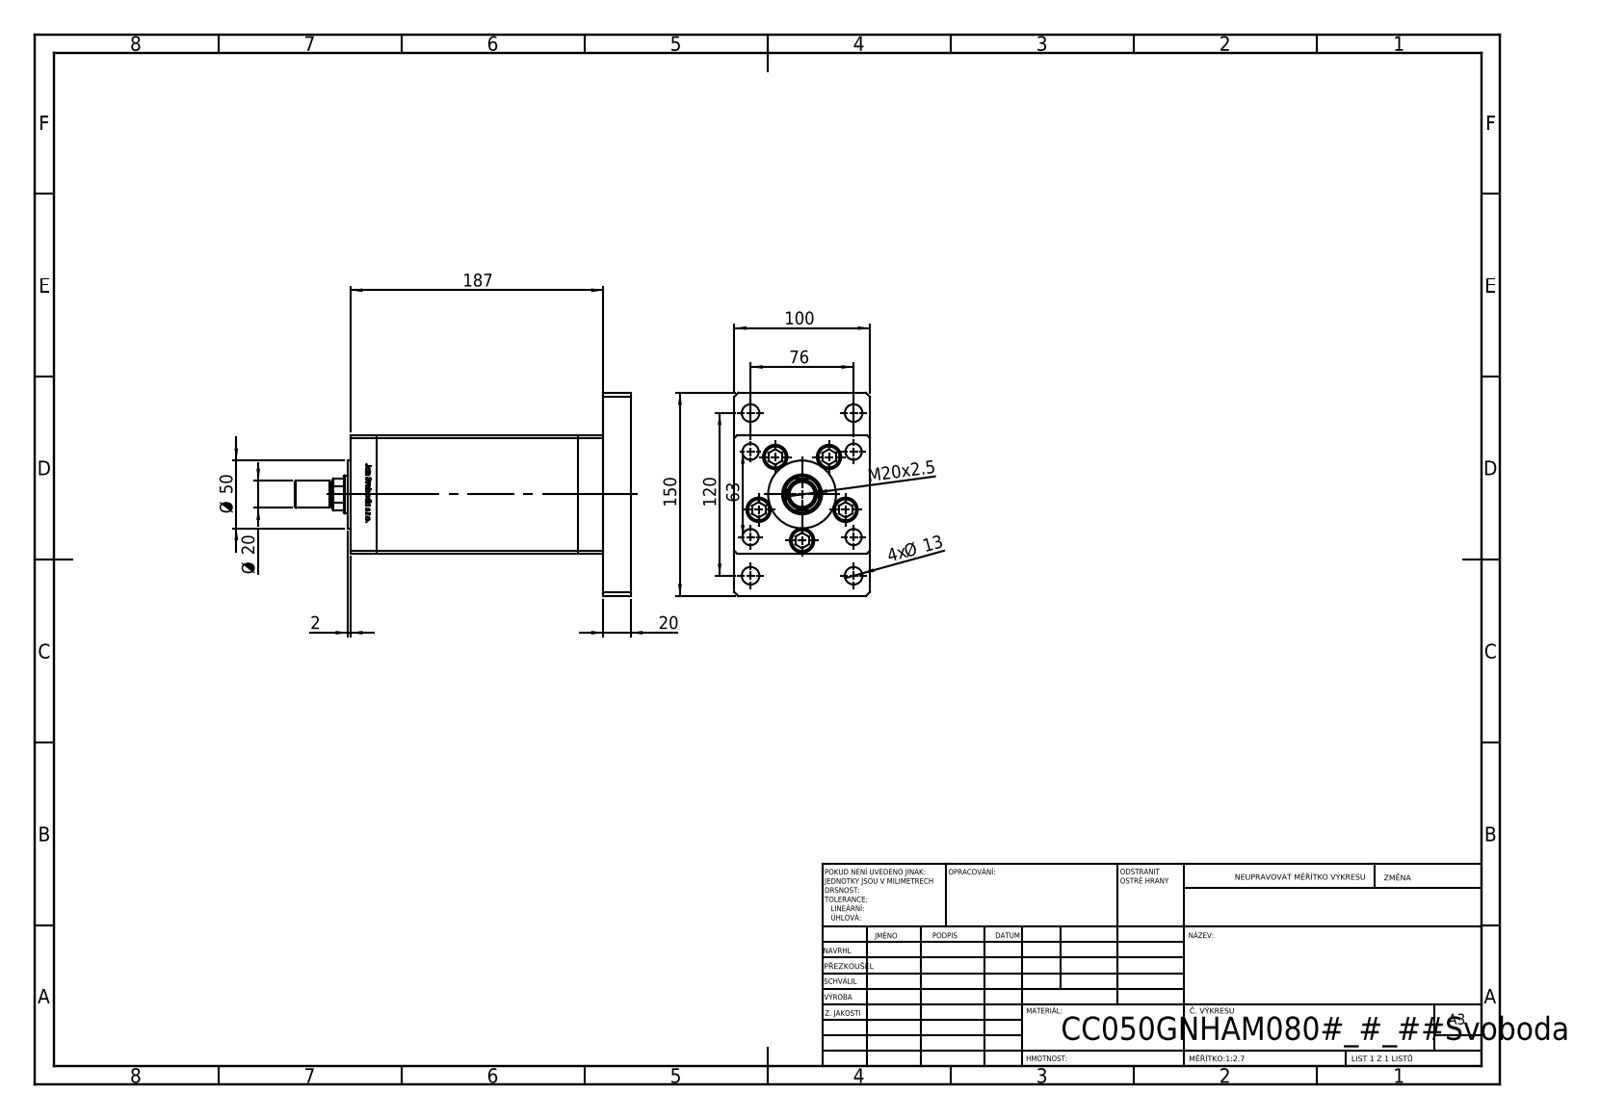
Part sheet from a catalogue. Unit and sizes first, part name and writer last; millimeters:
Units: millimetres
Overall size (bounding box): 247.5 × 150 × 100
Round holes (diameter × count): ⌀12 ×9, ⌀13.5 ×5, ⌀18 ×5, ⌀13 ×4, ⌀17 ×4, ⌀2 ×2, ⌀13.16 ×2, ⌀18.5 ×1, ⌀28 ×1, ⌀29.5 ×1, ⌀68 ×1
Round bosses / shafts (diameter × count): ⌀8 ×9, ⌀17 ×5, ⌀50 ×1, ⌀20 ×1, ⌀18 ×1
Partial cylindrical surfaces — rounded edges, fillets, slot ends (radius × count): R0.93 ×2, R13.5 ×1
Main face-to-face distances: 19, 100, 167.5, 87, 148.5, 20, 187.5, 39, 206.5, 186.5
Hole centre spacings: 34, 28.5, 49.36, 71.02, 76, 81.17, 91.5, 118.95
Volume: 1 706 000 mm³ · Surface area: 259 173 mm²
Bodies: 20 solids, 1322 faces (519 planar, 191 cylindrical, 612 other)
Part name (STEP PRODUCT): V220C BACK_G; V220C_VC_G; V220CC_MALE_METRIC; ALLEN BOLT (+3 more)
STEP written by: SolidWorks 2019 (CONFIG_CONTROL_DESIGN)
